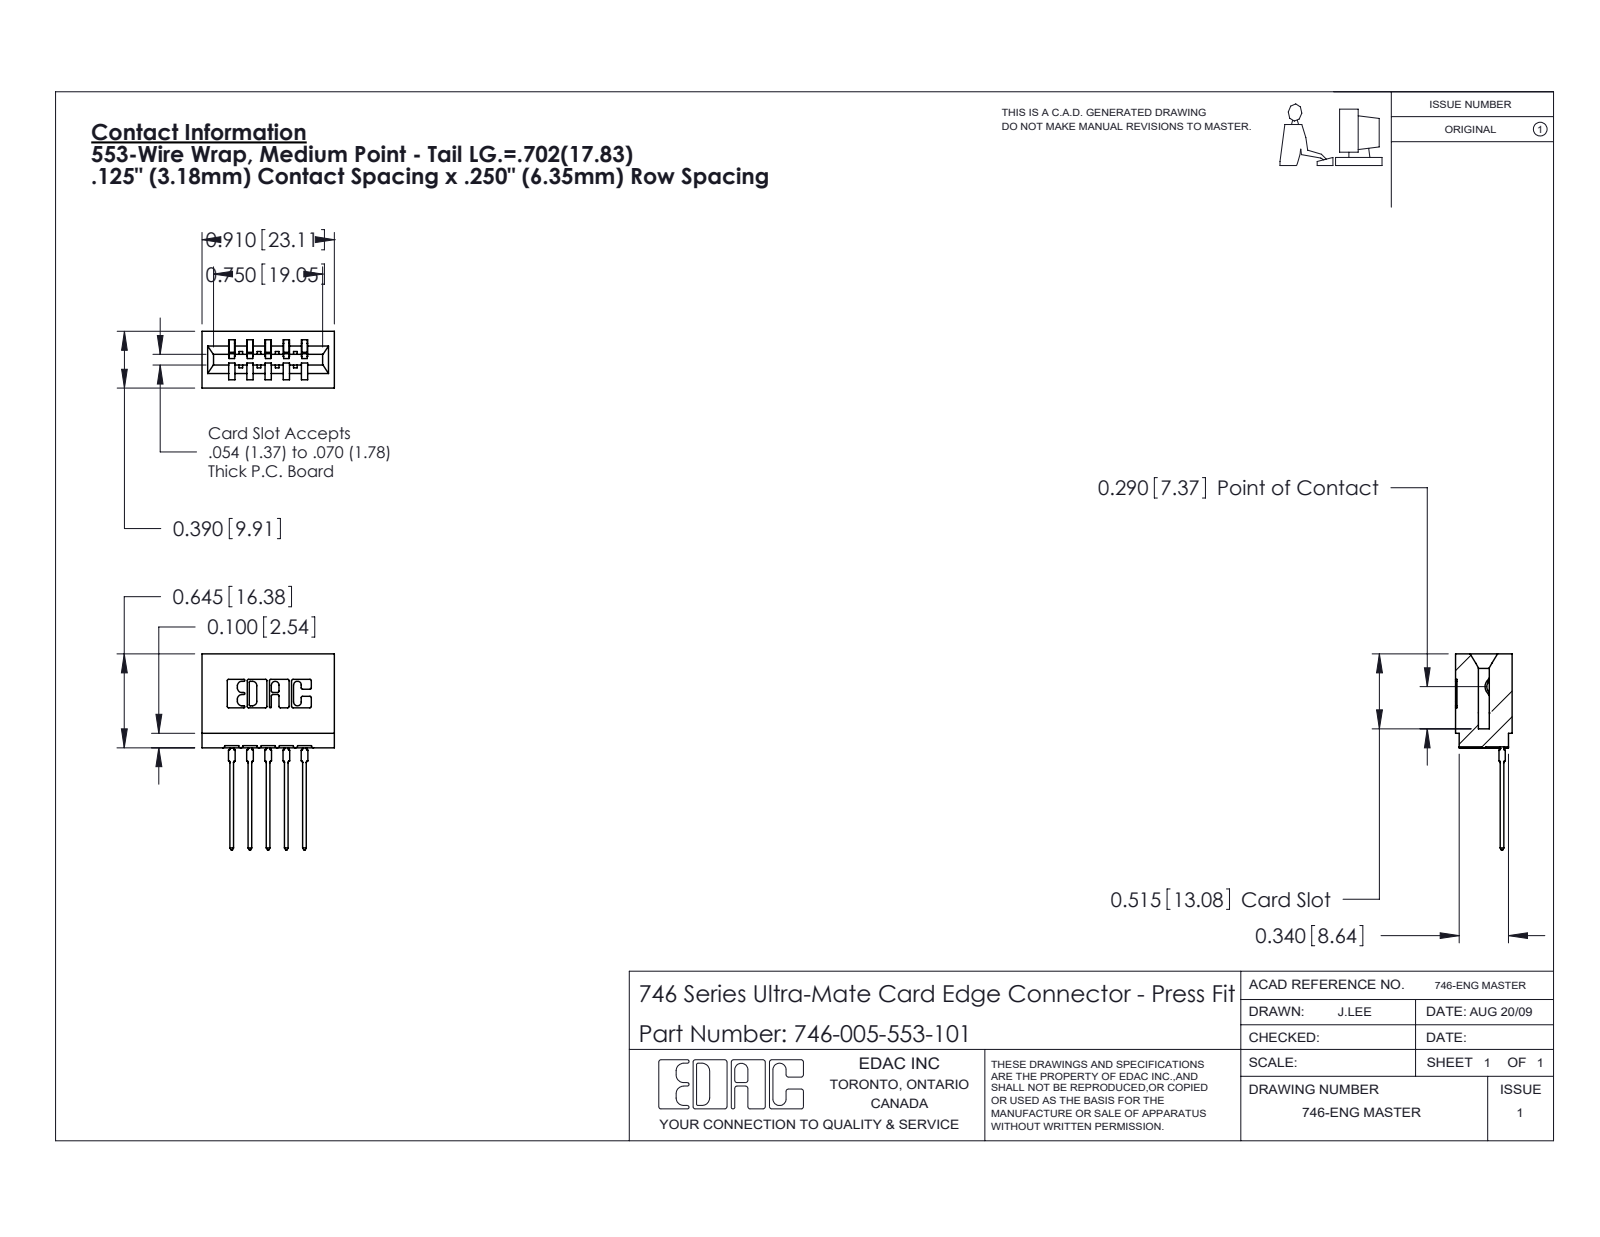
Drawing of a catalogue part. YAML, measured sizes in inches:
part_name: "746-292-001_553; 746-005-553-101; 746 Part_.515 Slot Depth - 01"
step_written_by: "SolidWorks 2020 (CONFIG_CONTROL_DESIGN)"
units: inches
bodies: {solids: 6, faces: 637, planar: 370, cylindrical: 137, other: 130}
overall_size: [1.346, 0.91, 0.39]
volume: 0.164
surface_area: 5.35
partial_cylinders:
  - {radius: 0.01, count: 22}
  - {radius: 0.021, count: 10}
  - {radius: 0.007, count: 6}
  - {radius: 0.015, count: 6}
  - {radius: 0.031, count: 6}
  - {radius: 0.005, count: 4}
  - {radius: 0.011, count: 4}
  - {radius: 0.026, count: 3}
face_to_face_distances: [0.25, 0.042, 0.333, 0.057, 0.125, 0.125, 0.39, 0.083, 0.208, 0.292]
